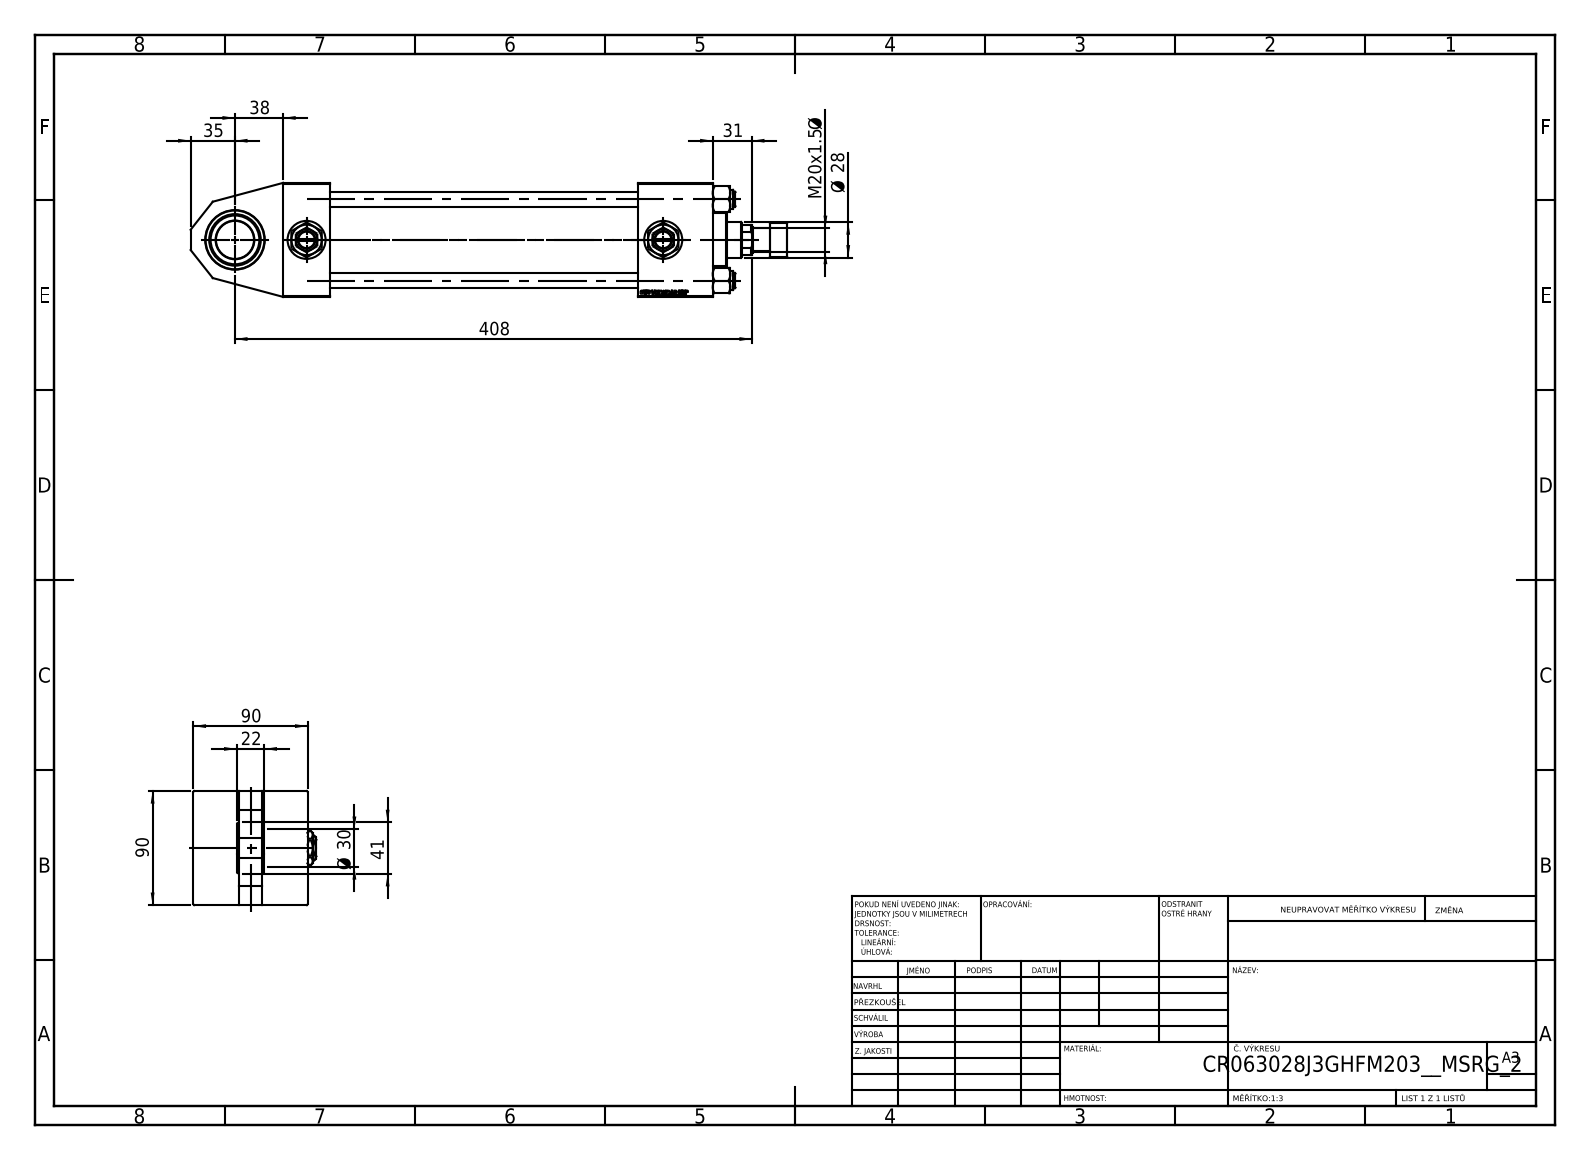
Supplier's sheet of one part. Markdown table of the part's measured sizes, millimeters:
| quantity | value |
| --- | --- |
| part name | V215_VC_A; V215CR_TYCINKA_J; V215CR_ROD_END_F; NUT_M5_J (+4 more) |
| STEP written by | SolidWorks 2019 (CONFIG_CONTROL_DESIGN) |
| units | millimeters |
| bodies | 15 solids, 1260 faces (568 planar, 104 cylindrical, 588 other) |
| overall size | 471 × 97 × 90 |
| volume | 1 347 000 mm³ |
| surface area | 328 281 mm² |
| round holes (diameter × count) | 12 × 4, 30 × 3, 2.5 × 2, 7 × 2, 20.96 × 2, 18.5 × 1, 28 × 1, 31 × 1, 47 × 1, 50 × 1, 60 × 1, 63 × 1 |
| round bosses / shafts (diameter × count) | 15 × 4, 69 × 1, 42 × 1, 27 × 1, 18 × 1 |
| main face-to-face distances | 90, 54, 36, 302, 37, 339, 59, 280, 243, 18 |
| hole center spacings | 32.39, 45.47, 64.3, 68.42, 28.25, 56.5, 90.93, 281.5 |
